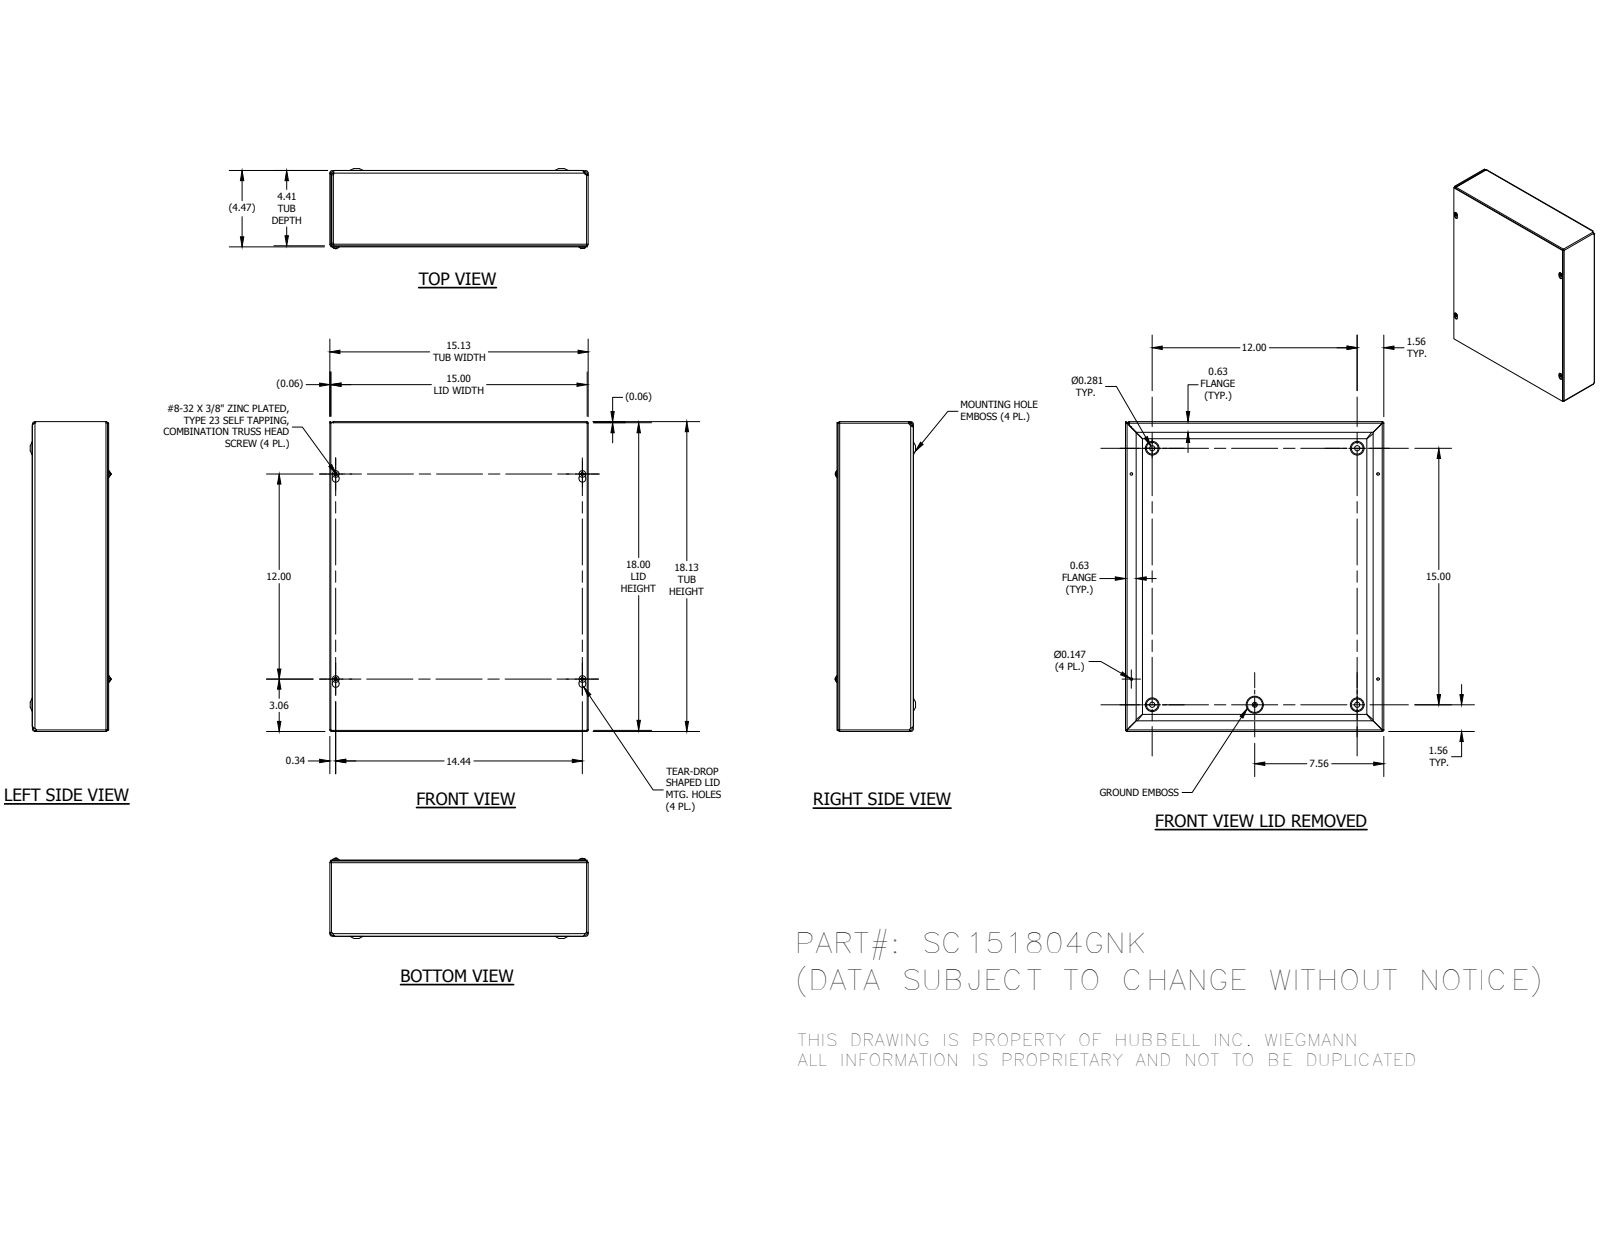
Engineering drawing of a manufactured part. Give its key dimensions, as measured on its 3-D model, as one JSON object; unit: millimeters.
{"part_name": "SC1518GNKBKP; SC151804GNKWRA; SC1518GNKLID; 34056 (+1 more)", "step_written_by": "Autodesk Inventor 2014 (AUTOMOTIVE_DESIGN)", "units": "millimeters", "bodies": {"solids": 7, "faces": 358, "planar": 133, "cylindrical": 73, "other": 152}, "overall_size": [460.38, 384.18, 119.2], "volume_mm3": 928281, "surface_area_mm2": 1188000, "round_holes": [[3.73, 4], [7.62, 4], [4.19, 1]], "round_bosses_or_shafts": [[9.75, 4], [4.17, 4], [5.8, 1]], "partial_cylinders_radius": [[0.79, 8], [2.37, 8], [1.4, 4], [1.57, 4], [2.38, 4], [2.97, 4], [3.15, 4], [3.17, 4]], "face_to_face_distances": [1.57, 110.32, 111.89, 1.59, 111.91, 113.48, 1.58, 384.18, 382.61, 382.6], "hole_center_spacings": [304.8, 152.4, 337.91, 344.27, 344.31, 366.71, 381, 410.35]}
